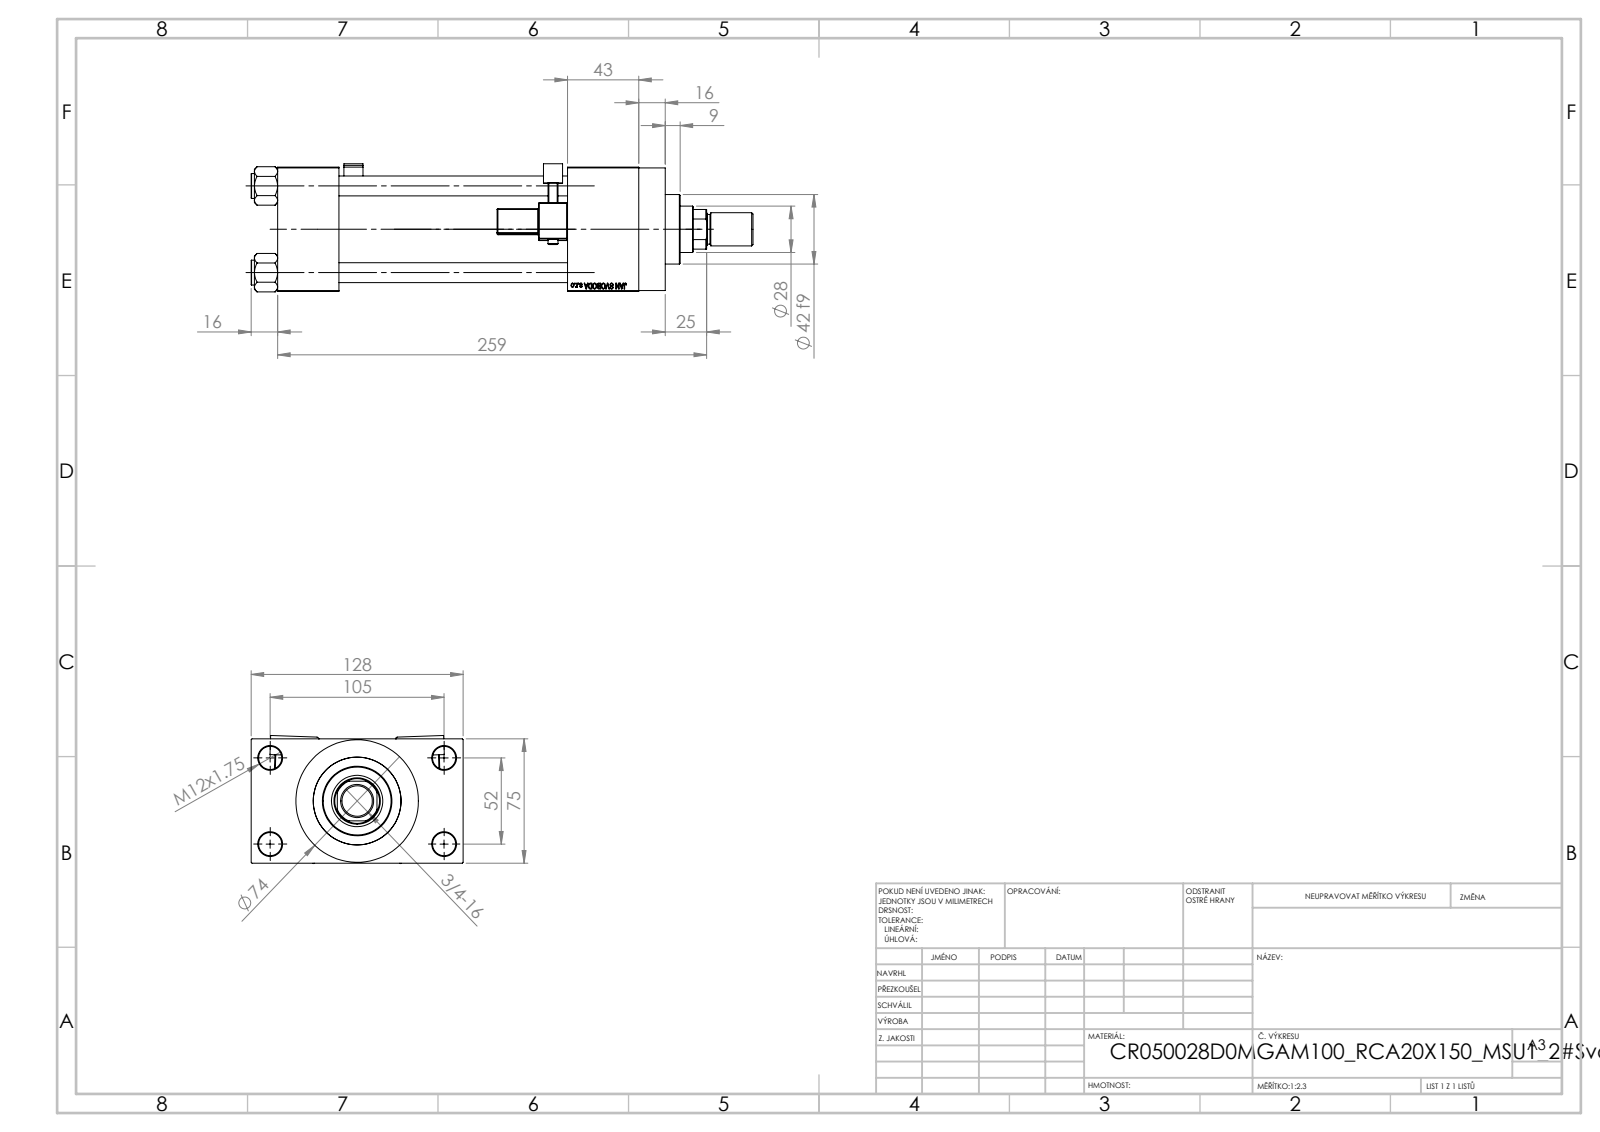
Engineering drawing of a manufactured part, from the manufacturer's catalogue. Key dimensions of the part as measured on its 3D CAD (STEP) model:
Part name (STEP PRODUCT): V215CR_D_TYCINKA; V215CR_D_Body; V215CR_VCP_D; V215_VC_A (+3 more)
STEP written by: SolidWorks 2019 (CONFIG_CONTROL_DESIGN)
Units: millimetres
Bodies: 14 solids, 1272 faces (559 planar, 153 cylindrical, 560 other)
Overall size (bounding box): 303 × 128 × 77.3
Volume: 990 443 mm³ · Surface area: 229 312 mm²
Round holes (diameter × count): ⌀12 ×4, ⌀14 ×4, ⌀7 ×2, ⌀20.96 ×2, ⌀30 ×2, ⌀18.5 ×1, ⌀28 ×1, ⌀31 ×1, ⌀41 ×1, ⌀50 ×1, ⌀53 ×1
Round bosses / shafts (diameter × count): ⌀15 ×4, ⌀6 ×2, ⌀74 ×1, ⌀56 ×1, ⌀42 ×1, ⌀20 ×1, ⌀18 ×1
Partial cylindrical surfaces — rounded edges, fillets, slot ends (radius × count): R0.5 ×48, R1 ×2, R2.5 ×2, R4 ×2, R13.5 ×1
Main face-to-face distances: 75, 138, 37, 175, 101.5, 26.5, 218, 181, 43, 16
Hole centre spacings: 26.35, 36.98, 52.3, 58.43, 58.59, 78.65, 94.37, 52
